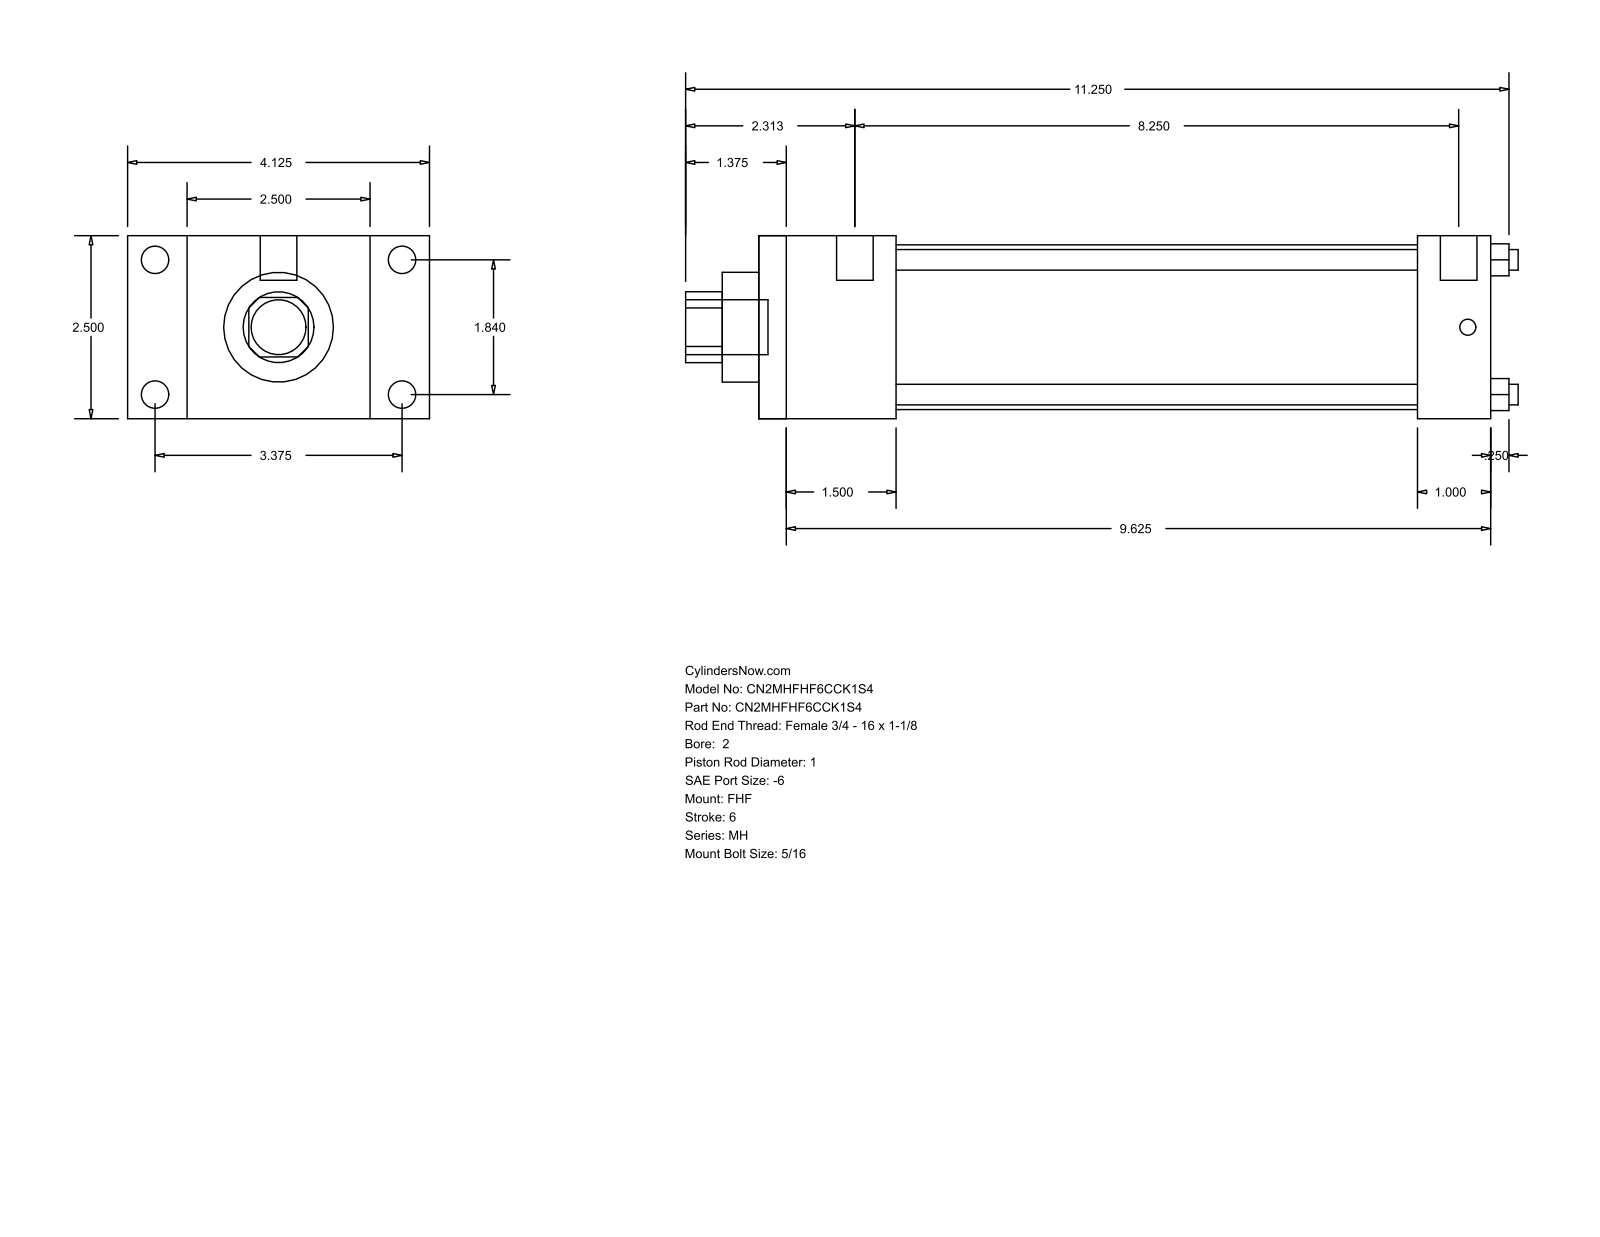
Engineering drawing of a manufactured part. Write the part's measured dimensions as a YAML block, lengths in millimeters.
part_name: "MH_FHF__0200_1"
step_written_by: "GSSL Pune (CONFIG_CONTROL_DESIGN)"
units: millimeters
bodies: {solids: 0, faces: 88, planar: 60, cylindrical: 28, other: 0}
overall_size: [288.93, 104.78, 63.5]
round_holes:
  - {diameter: 7.14, count: 4}
  - {diameter: 25.4, count: 1}
  - {diameter: 38.1, count: 1}
  - {diameter: 57.15, count: 1}
round_bosses_or_shafts:
  - {diameter: 9.53, count: 4}
  - {diameter: 5.56, count: 4}
  - {diameter: 12.7, count: 2}
  - {diameter: 19.05, count: 1}
partial_cylinders:
  - {radius: 12.29, count: 1}
face_to_face_distances: [63.5, 254, 47.63, 206.37, 20.64, 84.14, 104.78, 25.4, 228.6, 180.97]
hole_center_spacings: [33.05, 46.74, 66.1]
